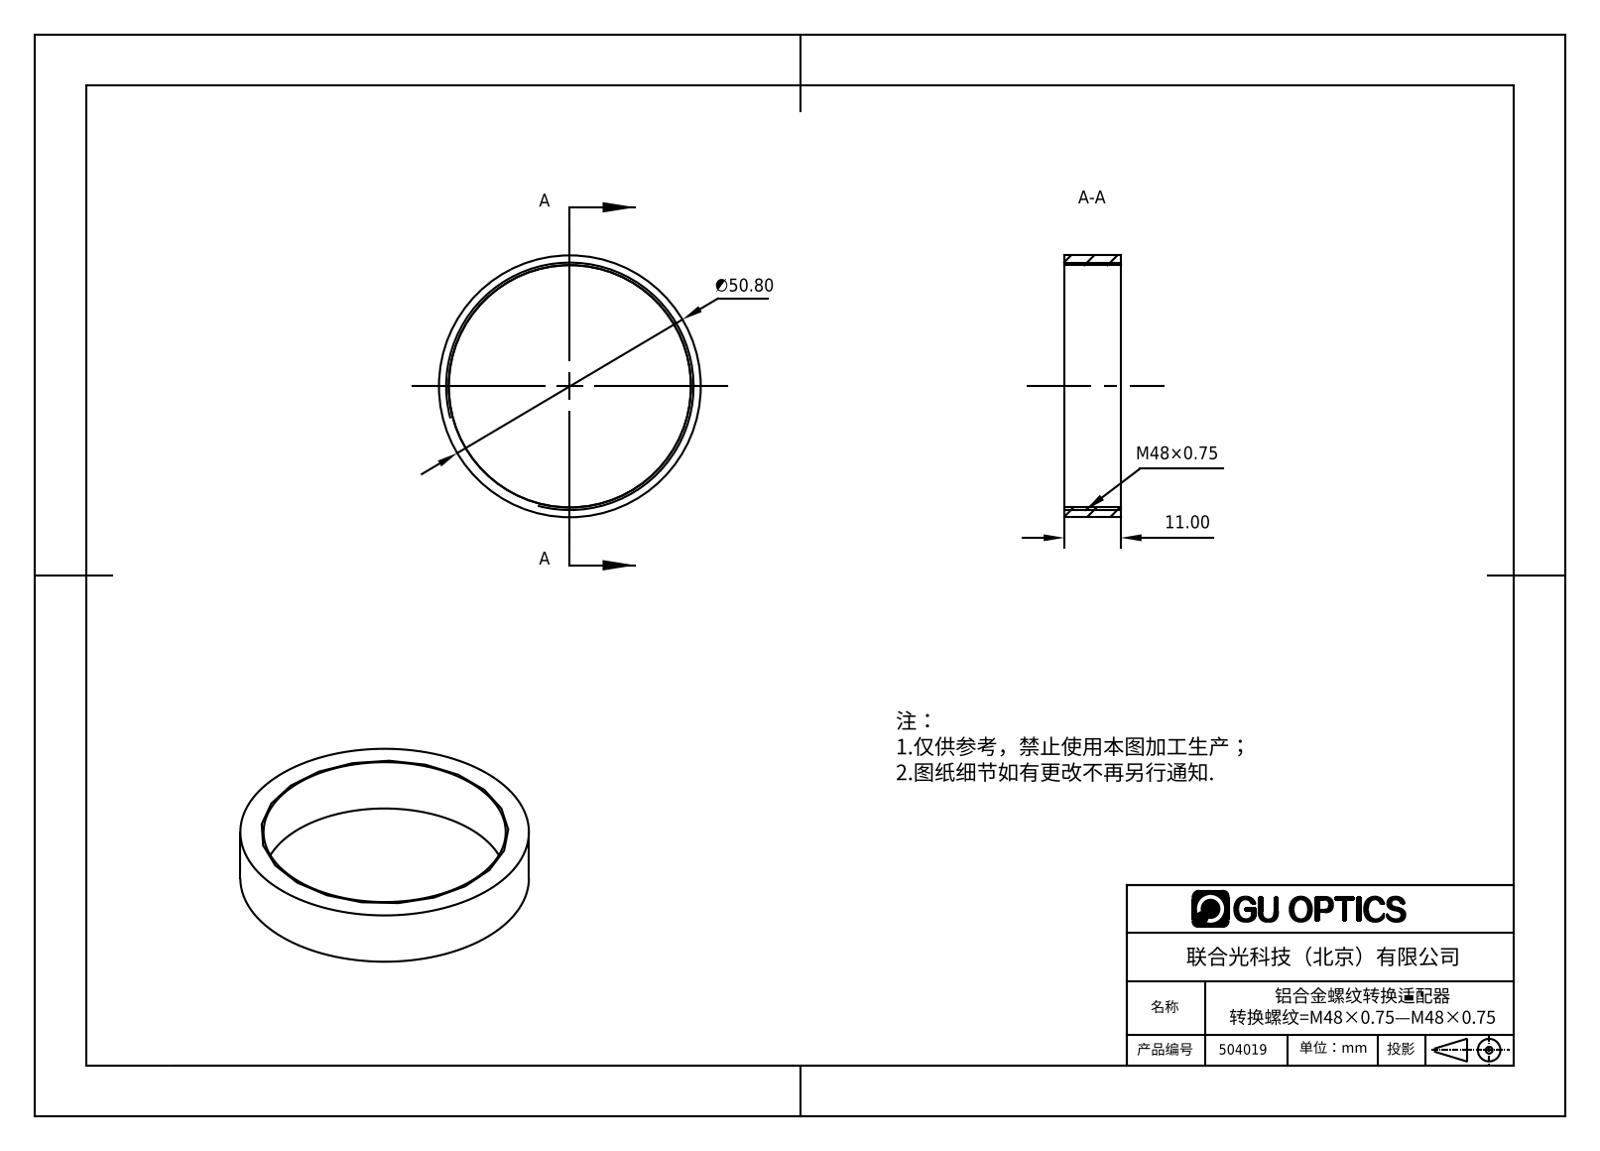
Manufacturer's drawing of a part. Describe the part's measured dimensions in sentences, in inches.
The part is named "504019". Its 3-D file was written by "SolidWorks 2016 (AUTOMOTIVE_DESIGN)". It is 1 solid with 6 faces: 2 planar, 4 cylindrical and 0 other. Overall it measures 2 by 2 by 0.433 inches. Its volume is 0.196 cubic inches and its surface area 6.144 square inches. Round holes: 1 of diameter 1.85. Round bosses or shafts: 1 of diameter 2. The main face-to-face distances are 0.433.
